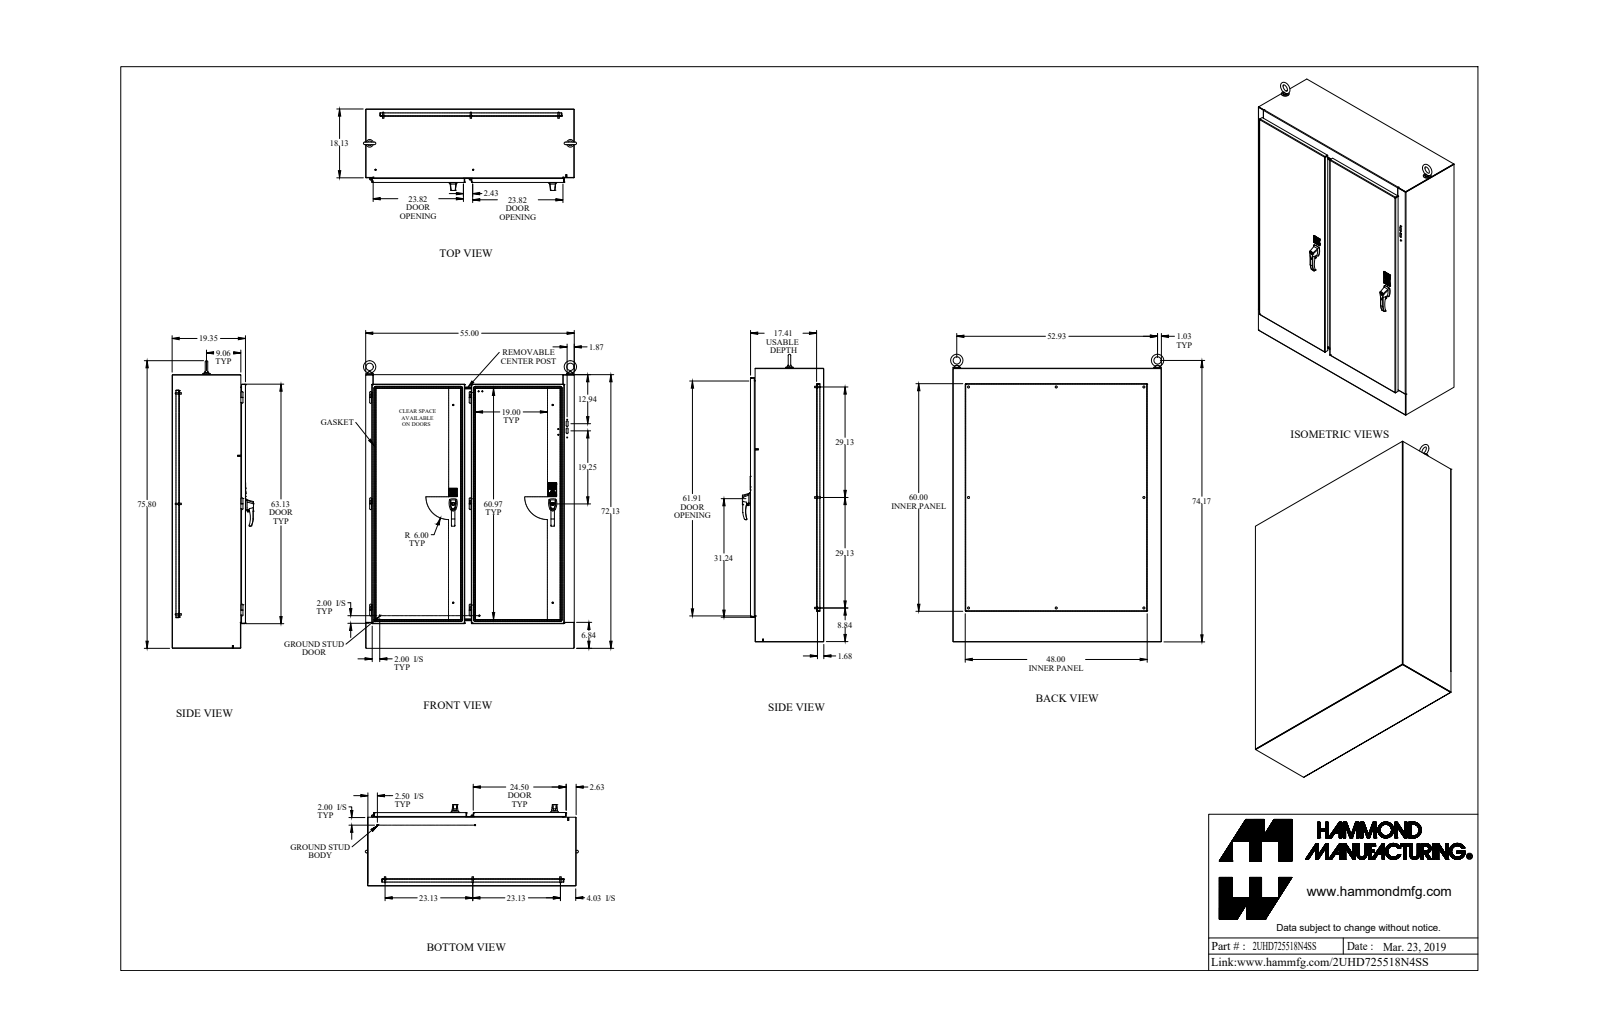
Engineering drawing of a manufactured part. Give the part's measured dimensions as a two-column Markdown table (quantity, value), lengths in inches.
| quantity | value |
| --- | --- |
| part name | 2UHD725518N4SS |
| STEP written by | SolidWorks 2018 (AUTOMOTIVE_DESIGN) |
| units | inches |
| bodies | 223 solids, 3376 faces (1951 planar, 1018 cylindrical, 407 other) |
| overall size | 75.799 × 56.182 × 21.466 |
| volume | 3 104 in³ |
| surface area | 38 083 in² |
| round holes (diameter × count) | 0.25 × 15, 0.196 × 13, 0.281 × 9, 0.307 × 9, 0.35 × 8, 0.201 × 6, 0.257 × 6, 0.313 × 6, 0.313 × 6, 0.255 × 5, 0.445 × 5, 0.156 × 4 |
| round bosses / shafts (diameter × count) | 0.25 × 20, 1 × 14, 0.65 × 9, 0.375 × 8, 0.332 × 8, 0.75 × 6, 0.625 × 6, 0.5 × 6 |
| partial cylindrical surfaces (radius × count) | 0.125 × 67, 0.5 × 38, 0.017 × 32, 0.048 × 32, 0.143 × 32, 0.06 × 29, 0.03 × 28, 0.25 × 26 |
| main face-to-face distances | 0.095, 0.072, 17.461, 19.368, 19.273, 1.907, 1.812, 1.835, 1.74, 17.533 |
| hole center spacings | 26.25, 27.188, 1.72, 1.72, 3.43, 24.937, 26.274, 36.207 |
